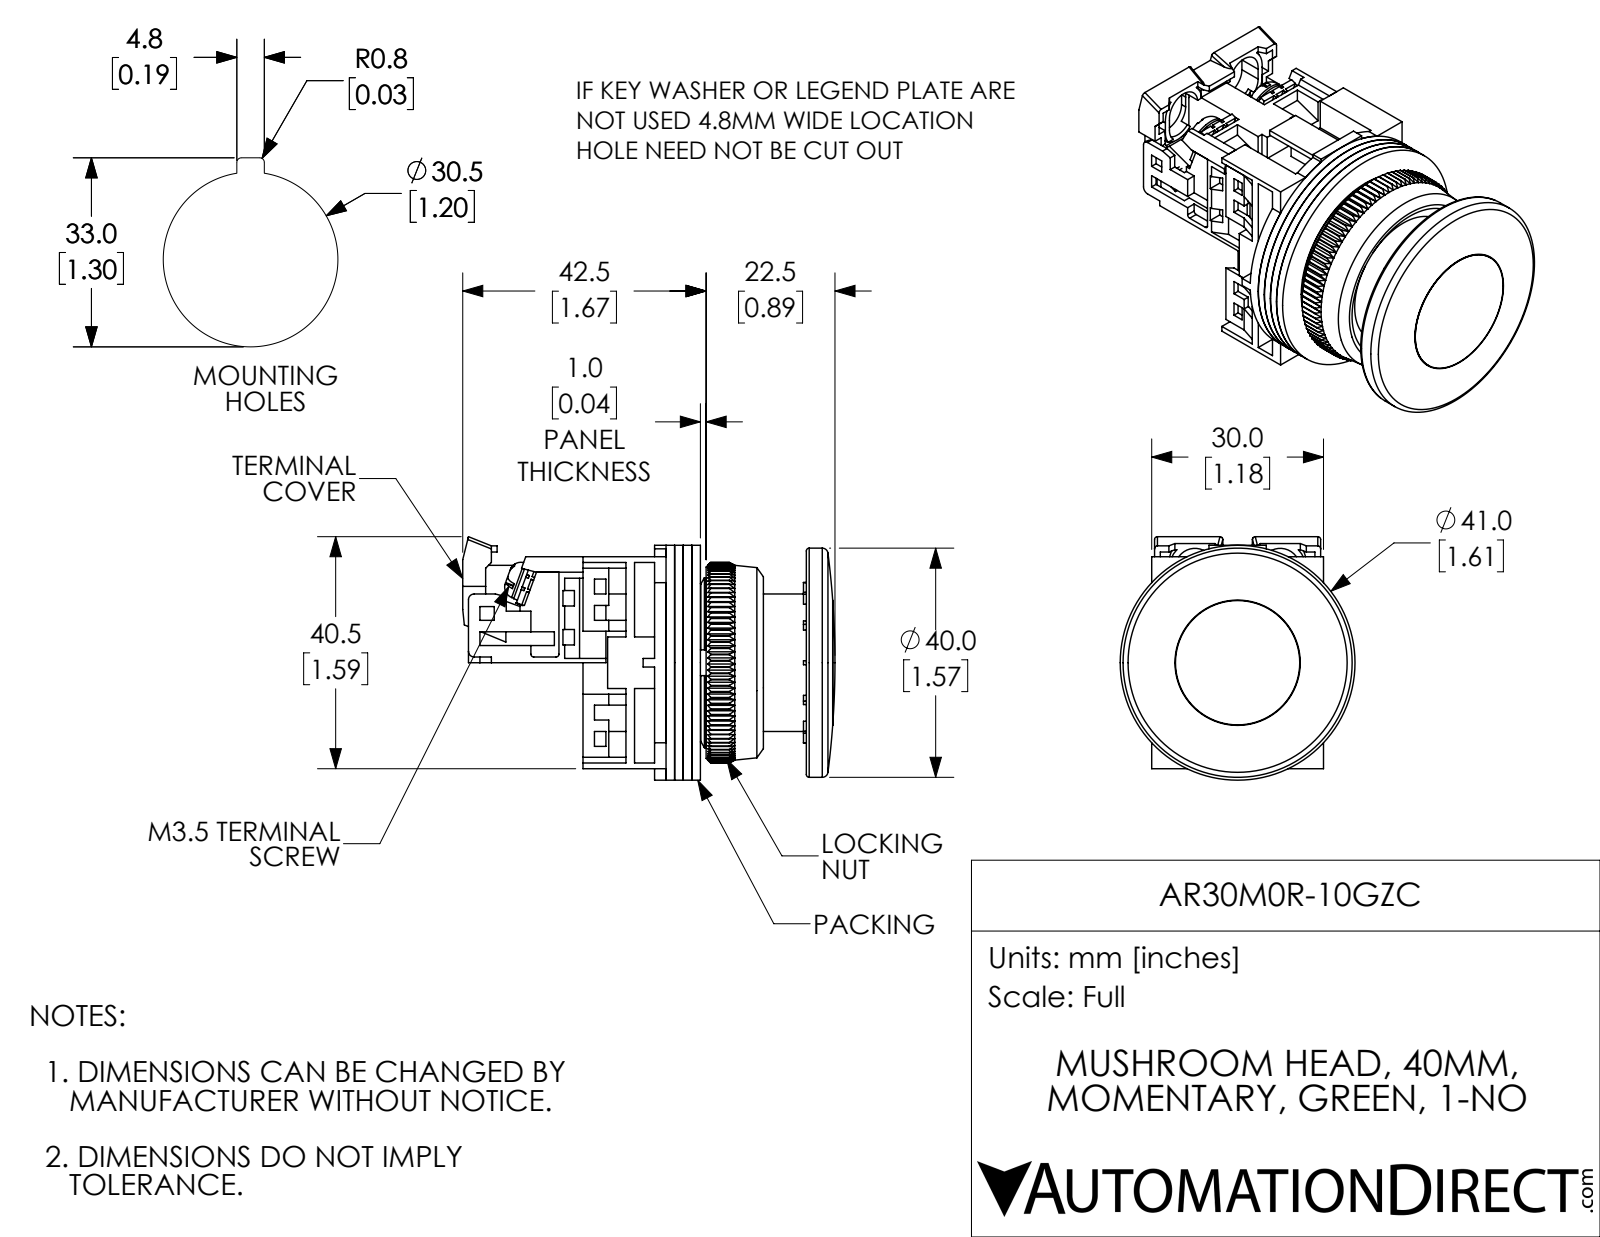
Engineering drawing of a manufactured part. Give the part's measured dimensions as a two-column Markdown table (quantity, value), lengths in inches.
| quantity | value |
| --- | --- |
| part name | AR30M0R-10GZC |
| STEP written by | SolidWorks 2017 (AUTOMOTIVE_DESIGN) |
| units | inches |
| bodies | 15 solids, 1278 faces (819 planar, 260 cylindrical, 199 other) |
| overall size | 2.559 × 1.673 × 1.614 |
| volume | 2.225 in³ |
| surface area | 48.33 in² |
| round holes (diameter × count) | 0.138 × 4, 0.142 × 2, 0.118 × 1, 0.709 × 1, 0.945 × 1, 1.122 × 1, 1.252 × 1, 1.417 × 1 |
| round bosses / shafts (diameter × count) | 0.26 × 2, 0.138 × 2, 1.614 × 1, 1.575 × 1, 1.181 × 1, 0.854 × 1 |
| partial cylindrical surfaces (radius × count) | 0.059 × 8, 0.02 × 6, 0.039 × 2, 0.138 × 2, 0.177 × 2, 0.118 × 1, 0.398 × 1, 0.449 × 1 |
| main face-to-face distances | 0.059, 0.118, 0.177, 0.039, 0.079, 0.689, 0.728, 0.866, 0.807, 1.417 |
| hole center spacings | 0.579, 0.61 |
